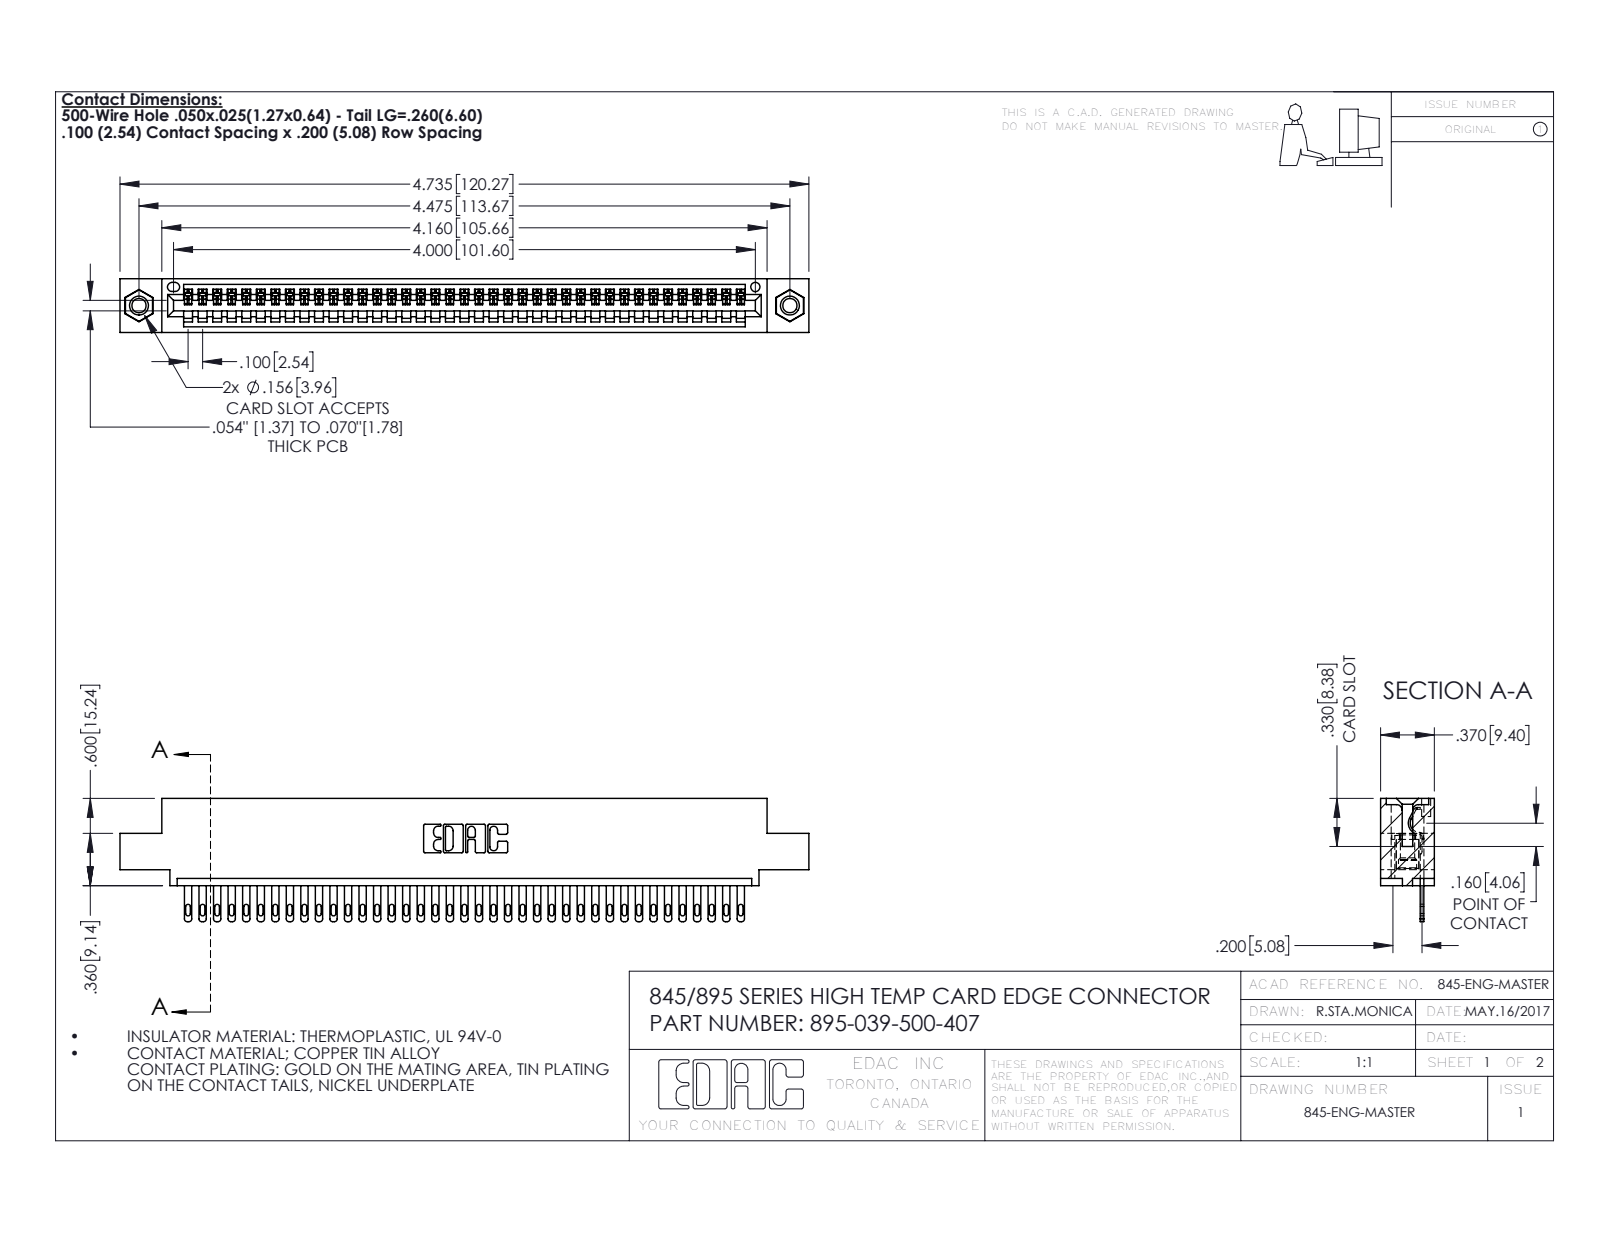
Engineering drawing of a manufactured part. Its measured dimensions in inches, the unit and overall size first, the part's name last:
Units: inches
Overall size (bounding box): 4.735 × 0.847 × 0.37
Round holes (diameter × count): ⌀0.098 ×2, ⌀0.125 ×2, ⌀0.156 ×2, ⌀0.064 ×1
Round bosses / shafts (diameter × count): ⌀0.155 ×2
Partial cylindrical surfaces — rounded edges, fillets, slot ends (radius × count): R0.006 ×78, R0.016 ×78, R0.02 ×78, R0.01 ×22, R0.007 ×6, R0.031 ×6, R0.026 ×3, R0.031 ×2
Main face-to-face distances: 0.072, 0.298, 0.37, 0.098, 0.272, 0.025, 0.2, 0.225, 0.149, 0.072
Hole centre spacings: 0.27, 4.239, 4.475
Volume: 0.692 in³ · Surface area: 23.6 in²
Bodies: 42 solids, 2296 faces (1442 planar, 838 cylindrical, 16 other)
Part name (STEP PRODUCT): 895-039-500-407; 345-250-001_345-250-005-103; 345-292-001_345-293-100; 845 Part_0.110 Offset - 0.156 Dia-TI
STEP written by: SolidWorks 2020 (CONFIG_CONTROL_DESIGN)
